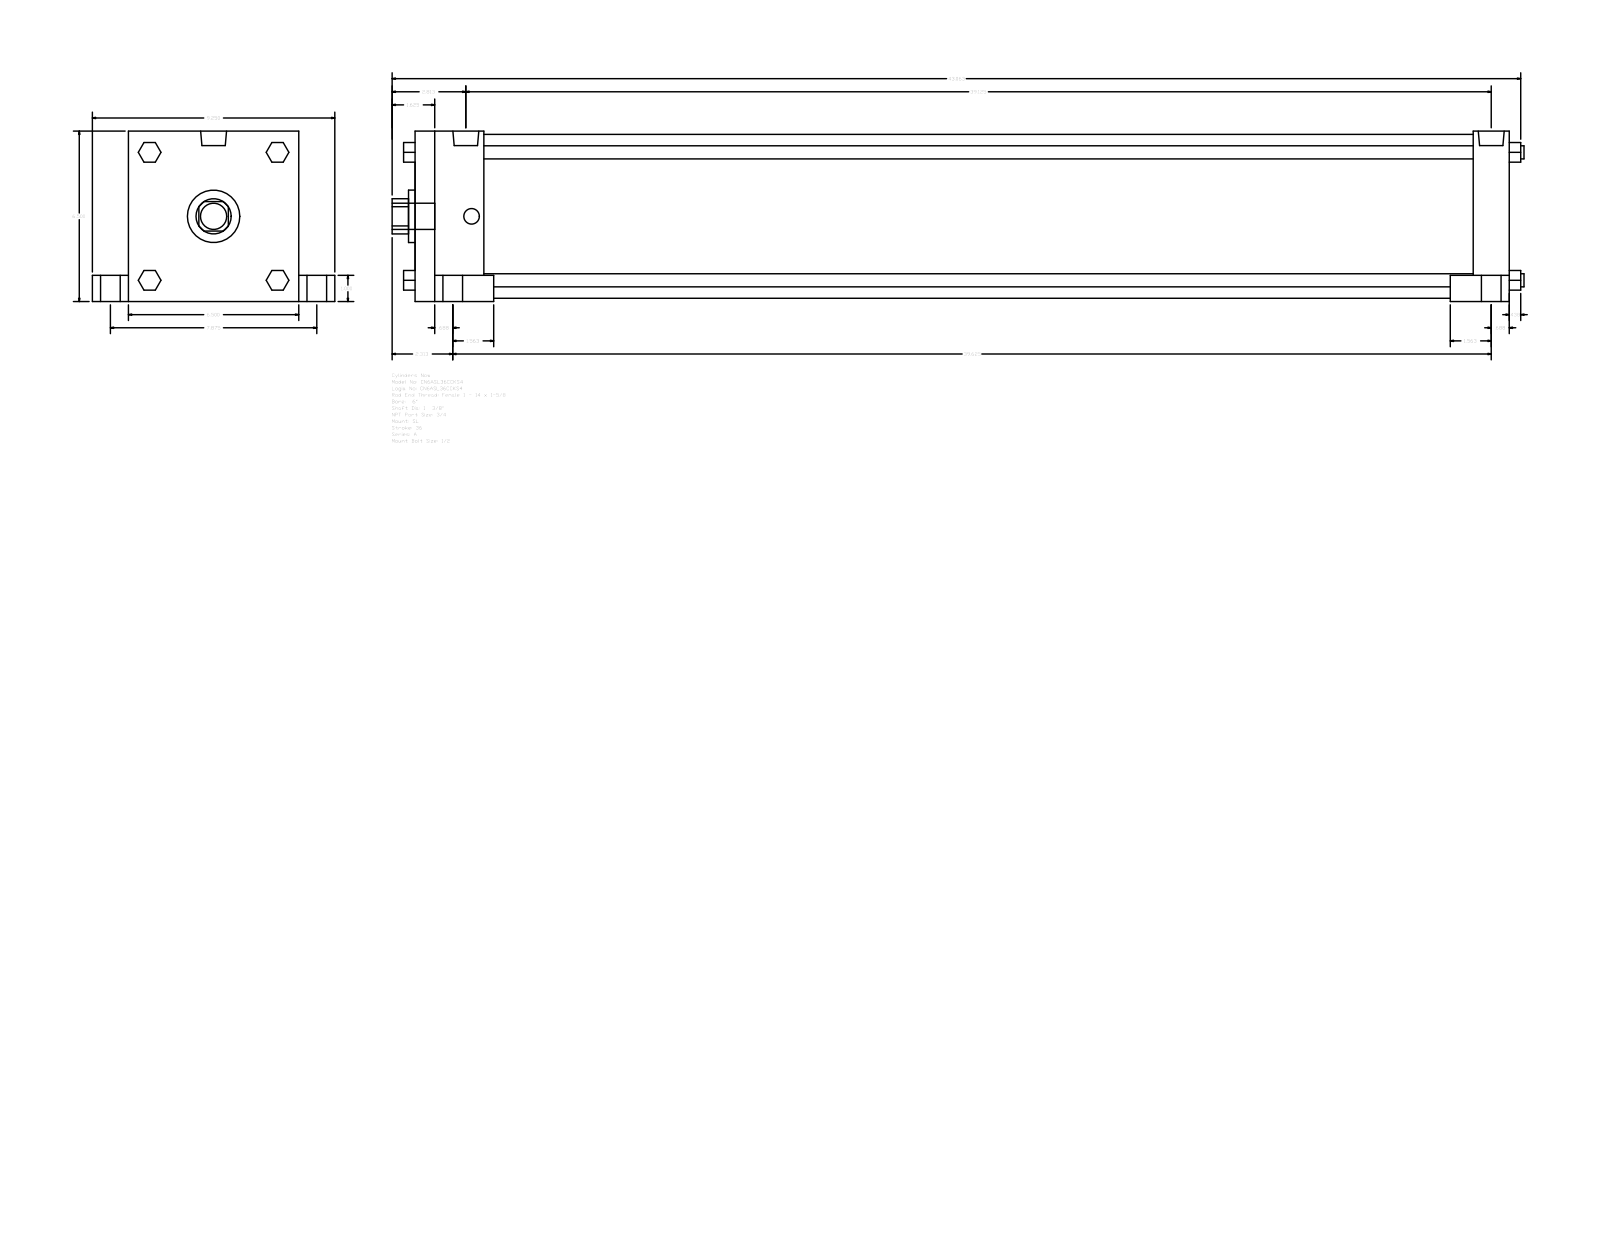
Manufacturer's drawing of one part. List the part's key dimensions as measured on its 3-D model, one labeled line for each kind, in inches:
Part name (STEP PRODUCT): A_SL__0600_1.375
STEP written by: GSSL Pune (CONFIG_CONTROL_DESIGN)
Units: inches
Bodies: 0 solids, 150 faces (114 planar, 36 cylindrical, 0 other)
Overall size (bounding box): 43.187 × 9.25 × 6.5
Round holes (diameter × count): ⌀1.375 ×1, ⌀2 ×1, ⌀6.25 ×1
Round bosses / shafts (diameter × count): ⌀1 ×5, ⌀0.75 ×4, ⌀0.594 ×4, ⌀0.5 ×4, ⌀0.989 ×2
Partial cylindrical surfaces — rounded edges, fillets, slot ends (radius × count): R0.672 ×1
Main face-to-face distances: 6.5, 41.75, 1.375, 2.625, 39.125, 40.375, 37.75, 1, 5.5, 7.875
